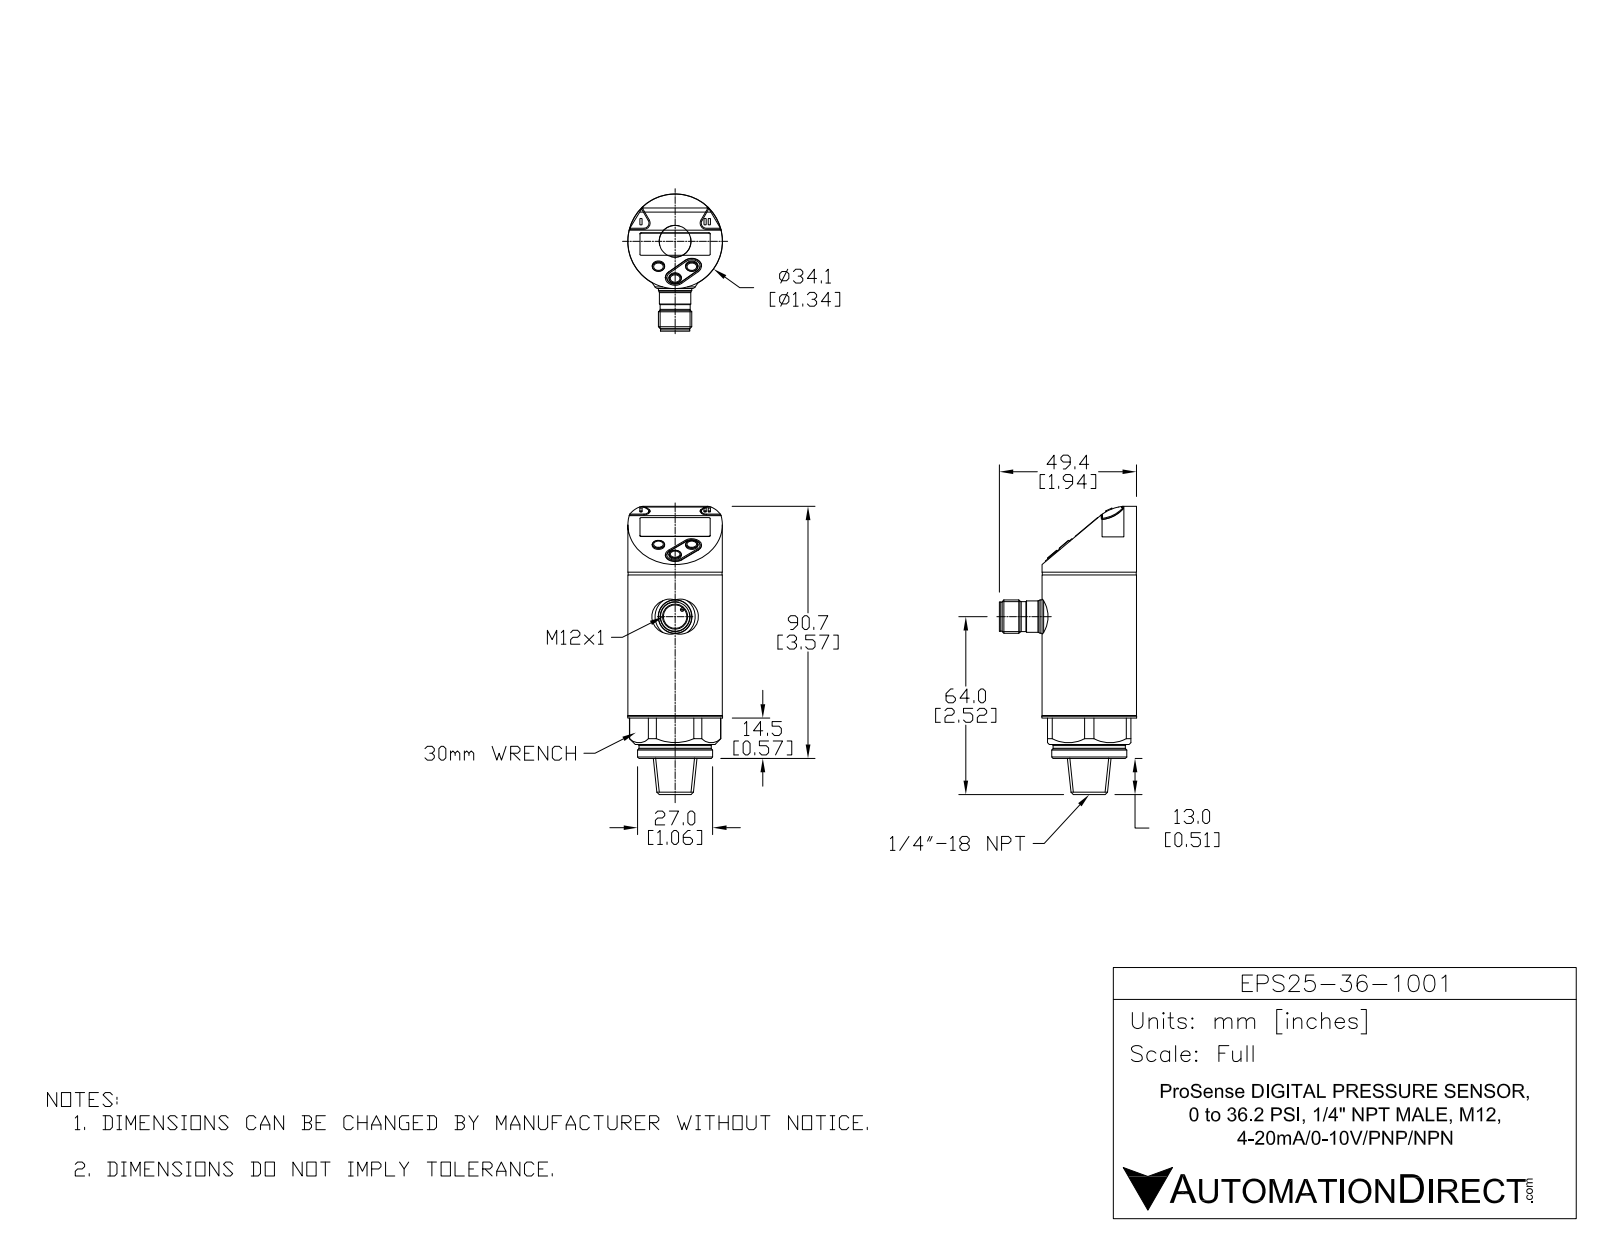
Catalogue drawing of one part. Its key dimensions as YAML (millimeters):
part_name: "EPS25-36-1001"
step_written_by: "SolidWorks 2016 (AUTOMOTIVE_DESIGN)"
units: millimeters
bodies: {solids: 11, faces: 370, planar: 207, cylindrical: 84, other: 79}
overall_size: [103.7, 49.4, 34.1]
volume: 72203
surface_area: 21365
round_holes:
  - {diameter: 4.2, count: 1}
  - {diameter: 8.45, count: 1}
round_bosses_or_shafts:
  - {diameter: 1.4, count: 4}
  - {diameter: 1, count: 4}
  - {diameter: 34.1, count: 1}
  - {diameter: 34, count: 1}
  - {diameter: 33.8, count: 1}
  - {diameter: 27, count: 1}
  - {diameter: 26, count: 1}
  - {diameter: 12, count: 1}
partial_cylinders:
  - {radius: 1.8, count: 2}
  - {radius: 2.2, count: 2}
  - {radius: 3, count: 2}
  - {radius: 3.5, count: 2}
  - {radius: 15, count: 2}
  - {radius: 0.61, count: 1}
  - {radius: 6.8, count: 1}
  - {radius: 16.44, count: 1}
face_to_face_distances: [0.68, 11.5, 12.18, 10.68, 1.5, 10, 2, 2.5, 14, 4]
